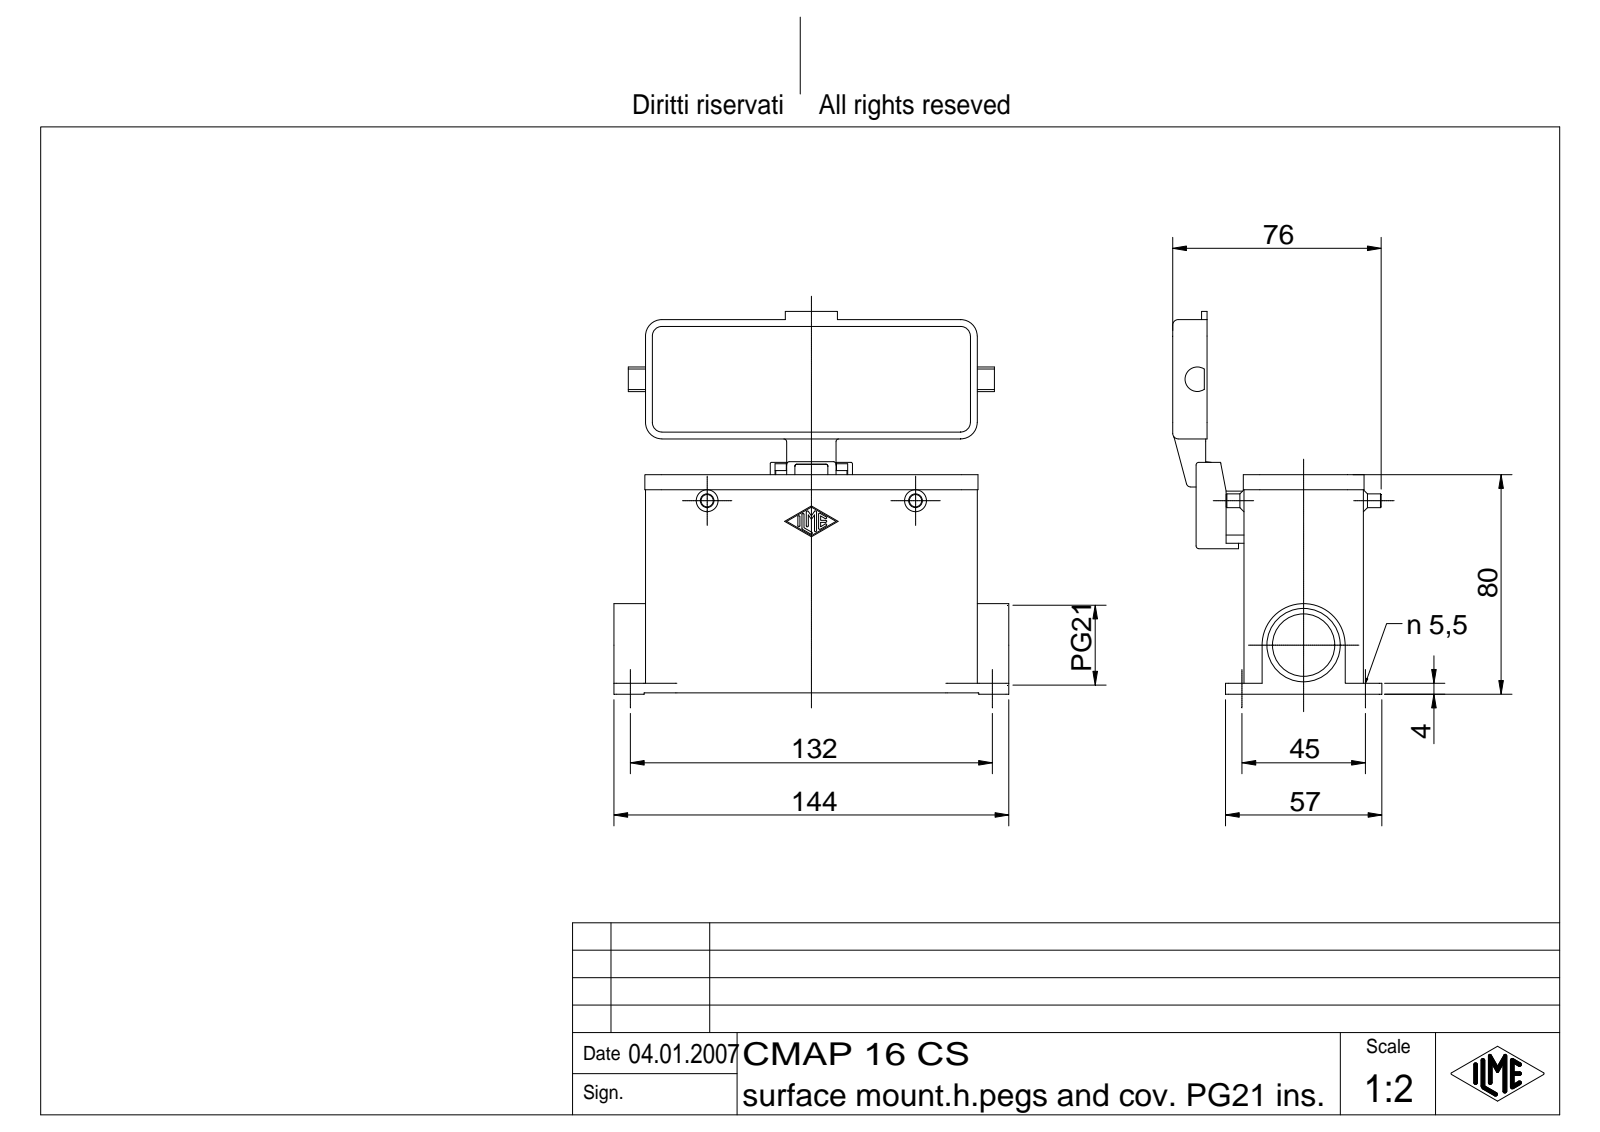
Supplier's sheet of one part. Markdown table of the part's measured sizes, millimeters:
| quantity | value |
| --- | --- |
| part name | CMAP 16 CS |
| STEP written by | Autodesk Inventor 7 (AUTOMOTIVE_DESIGN) |
| units | millimeters |
| bodies | 2 solids, 475 faces (177 planar, 177 cylindrical, 121 other) |
| overall size | 144 × 139.5 × 76.25 |
| volume | 162 396 mm³ |
| surface area | 88 802 mm² |
| round holes (diameter × count) | 5.5 × 4, 4 × 1, 5 × 1, 22.78 × 1, 26.78 × 1 |
| round bosses / shafts (diameter × count) | 5 × 2, 3 × 2, 7 × 1, 4 × 1 |
| partial cylindrical surfaces (radius × count) | 1 × 26, 0.38 × 14, 6 × 12, 0.5 × 9, 0.7 × 8, 2 × 8, 3 × 4, 3.5 × 4 |
| main face-to-face distances | 3, 40.5, 43.5, 3.5, 37.5, 69.5, 66.5, 22.5, 29, 26 |
| hole center spacings | 45, 132, 139.46 |
